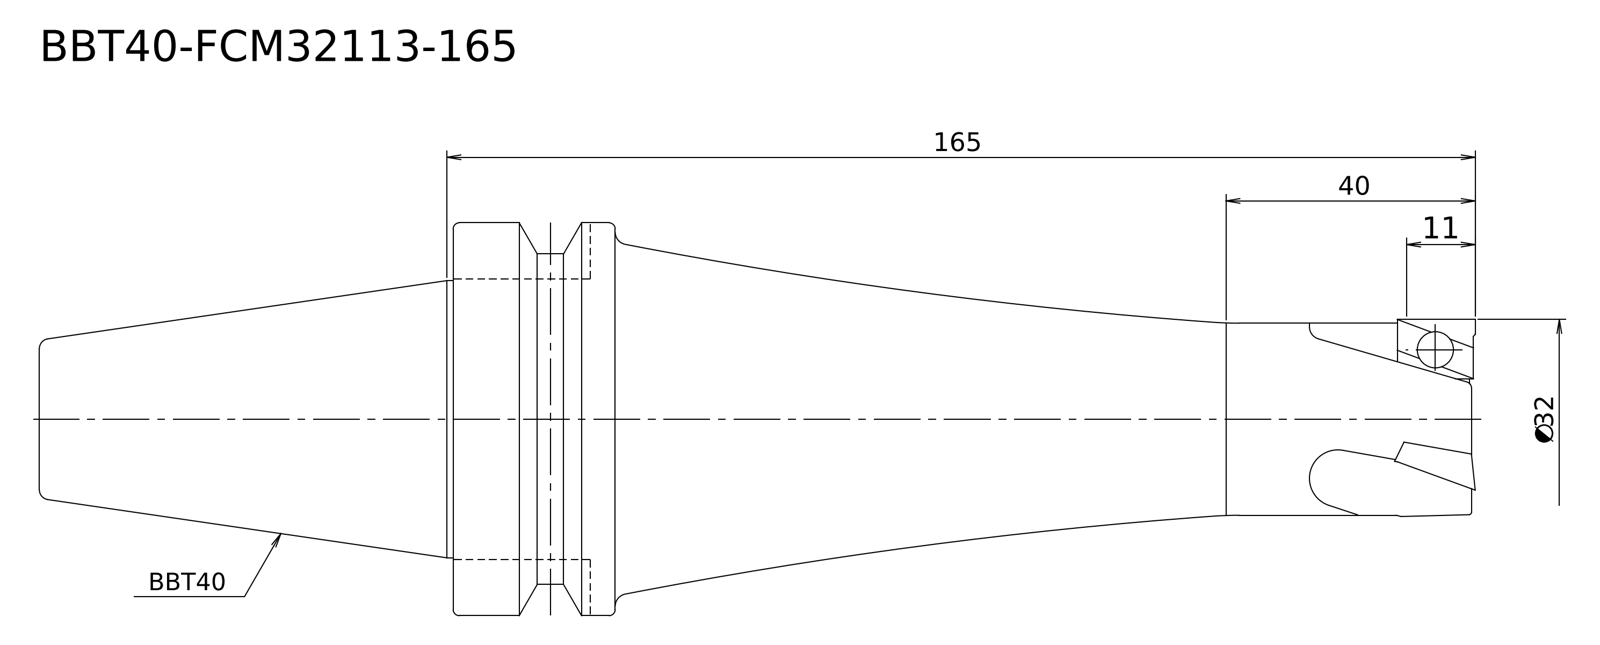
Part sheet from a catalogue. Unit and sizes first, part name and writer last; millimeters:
Units: millimetres
Overall size (bounding box): 230.4 × 63 × 63
Round bosses / shafts (diameter × count): ⌀63 ×1, ⌀53 ×1, ⌀44.45 ×1, ⌀32 ×1, ⌀30.8 ×1
Main face-to-face distances: 164, 230.4, 66.4, 138, 26, 92.4
Volume: 321 073 mm³ · Surface area: 34 144 mm²
Bodies: 1 solid, 17 faces (4 planar, 6 cylindrical, 7 other)
STEP written by: Kubotek KeyCreator V8.5.1 (14335) (CONFIG_CONTROL_DESIGN)
